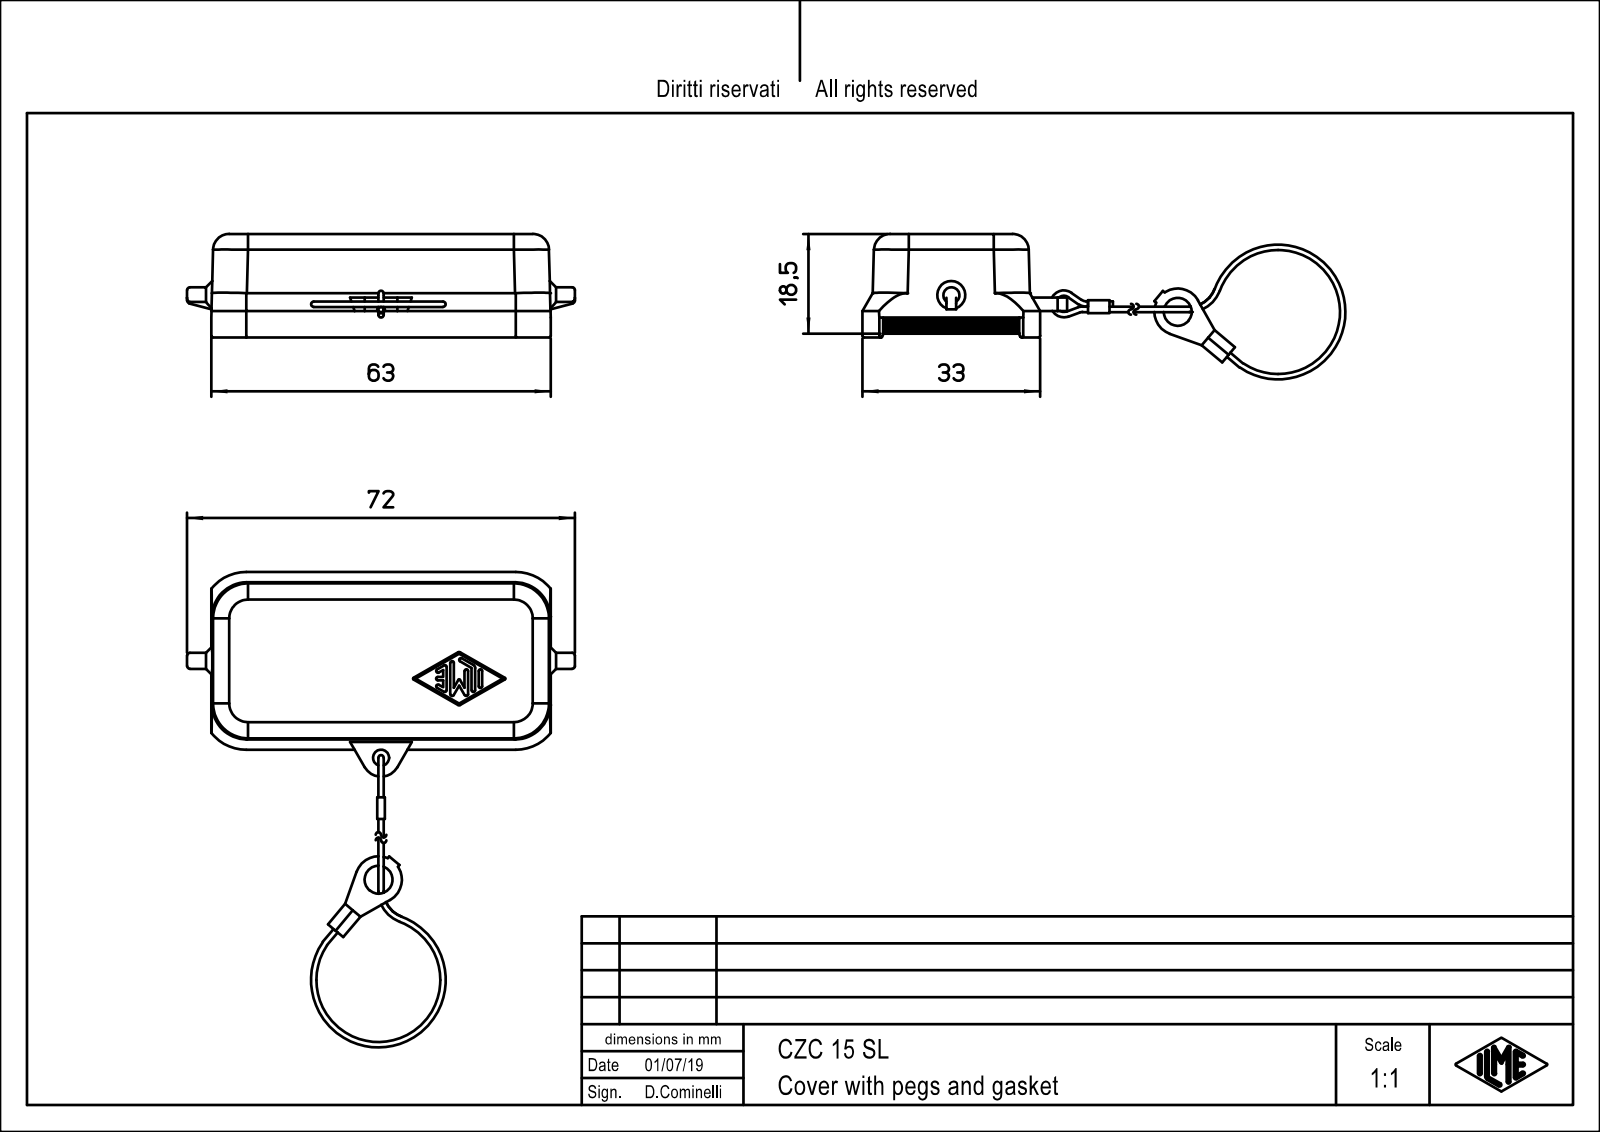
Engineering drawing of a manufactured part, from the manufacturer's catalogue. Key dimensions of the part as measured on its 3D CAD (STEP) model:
Part name (STEP PRODUCT): CZC_15_SL
STEP written by: Creo Elements/Direct Modeling 20.1B 02-Apr-2019 (C) Parametric Technology GmbH (AUTOMOTIVE_DESIGN)
Units: millimetres
Bodies: 1 solid, 147 faces (64 planar, 35 cylindrical, 48 other)
Overall size (bounding box): 72 × 38 × 19.2
Volume: 11 601 mm³ · Surface area: 10 963 mm²
Round holes (diameter × count): ⌀3 ×1
Round bosses / shafts (diameter × count): ⌀3 ×1
Partial cylindrical surfaces — rounded edges, fillets, slot ends (radius × count): R1 ×4, R3 ×4, R4.3 ×4, R5.3 ×4, R6 ×4, R6.5 ×4, R0.3 ×2, R0.5 ×2
Main face-to-face distances: 2.6, 2, 13.5, 15.5, 13.8, 1.2, 15.8, 31.8, 26.44, 33
